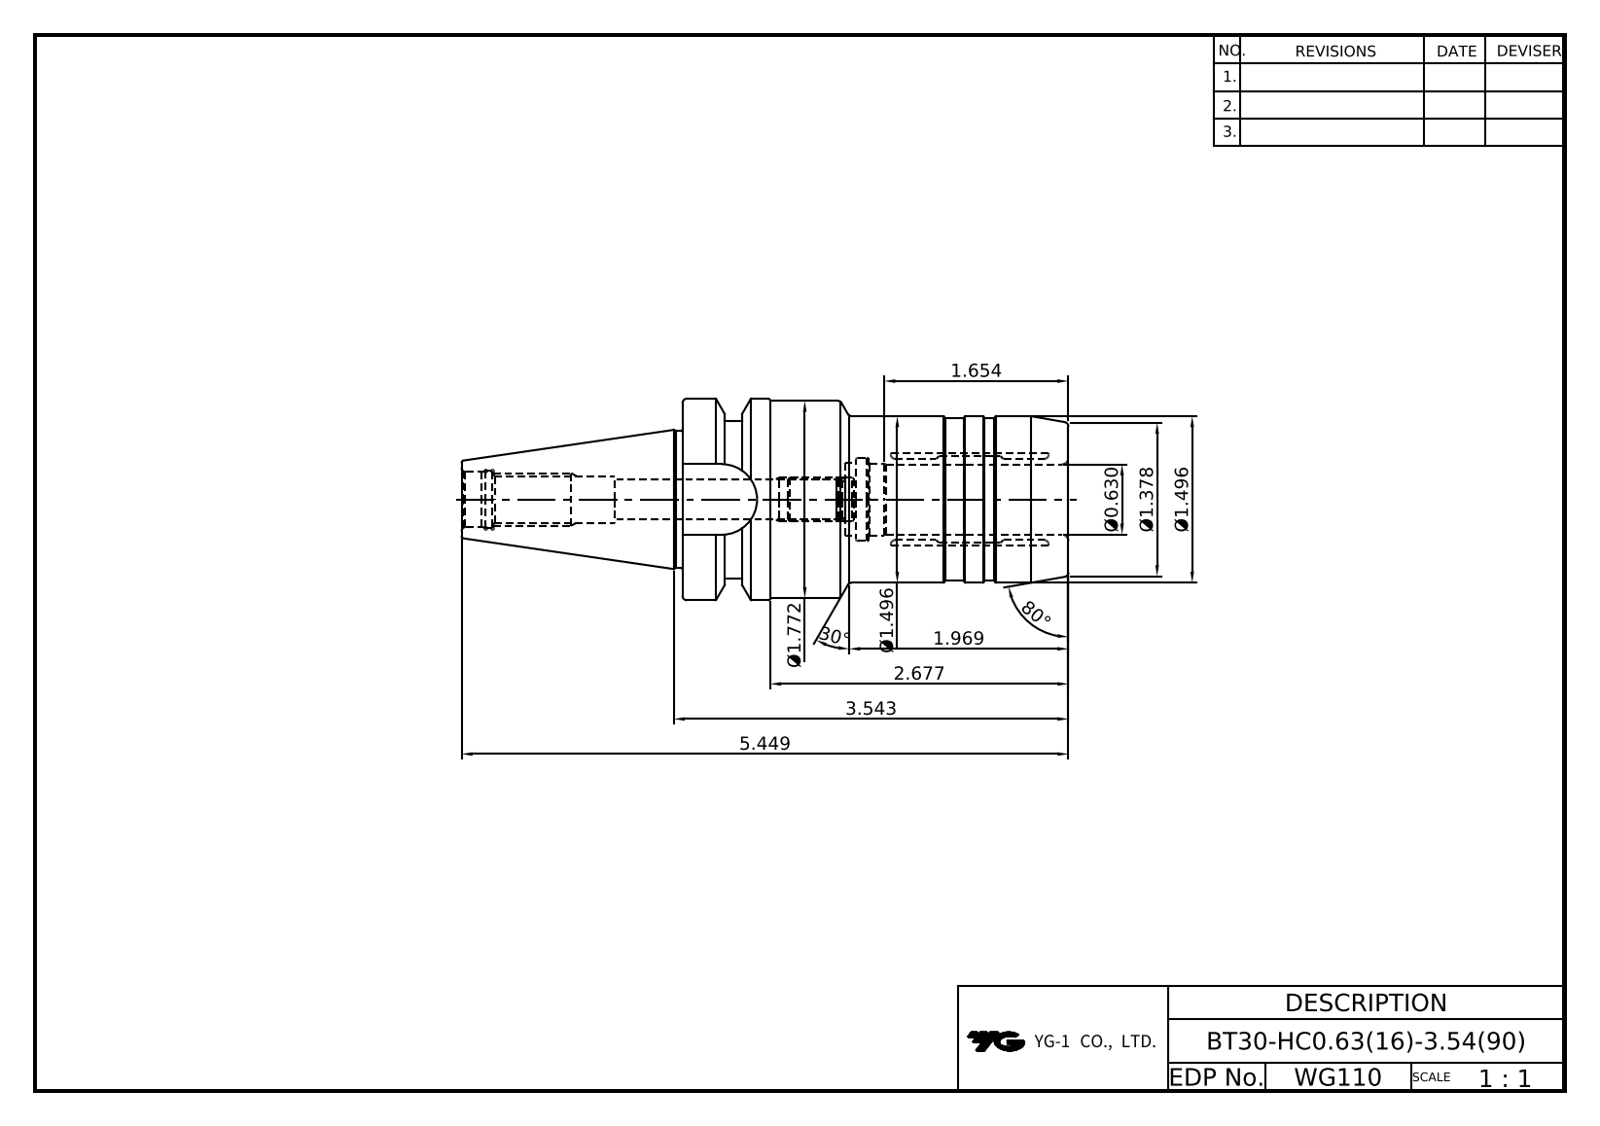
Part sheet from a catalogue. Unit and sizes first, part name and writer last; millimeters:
Units: millimetres
Overall size (bounding box): 138.4 × 46 × 46
Round holes (diameter × count): ⌀3.24 ×4, ⌀4 ×4, ⌀8.92 ×1, ⌀10.11 ×1, ⌀12.5 ×1, ⌀13.1 ×1, ⌀16 ×1, ⌀16.6 ×1
Round bosses / shafts (diameter × count): ⌀46 ×1, ⌀44.5 ×1, ⌀38 ×1, ⌀37 ×1, ⌀31.2 ×1
Partial cylindrical surfaces — rounded edges, fillets, slot ends (radius × count): R8.05 ×1, R18 ×1
Main face-to-face distances: 88, 32.6, 37, 51, 13.6, 23.4, 74.4, 9.6, 4, 27.4
Volume: 118 693 mm³ · Surface area: 23 973 mm²
Bodies: 1 solid, 93 faces (20 planar, 38 cylindrical, 35 other)
Part name (STEP PRODUCT): LO-BT30ADB-HC16-90
STEP written by: Autodesk Inventor 2022 (AUTOMOTIVE_DESIGN)
